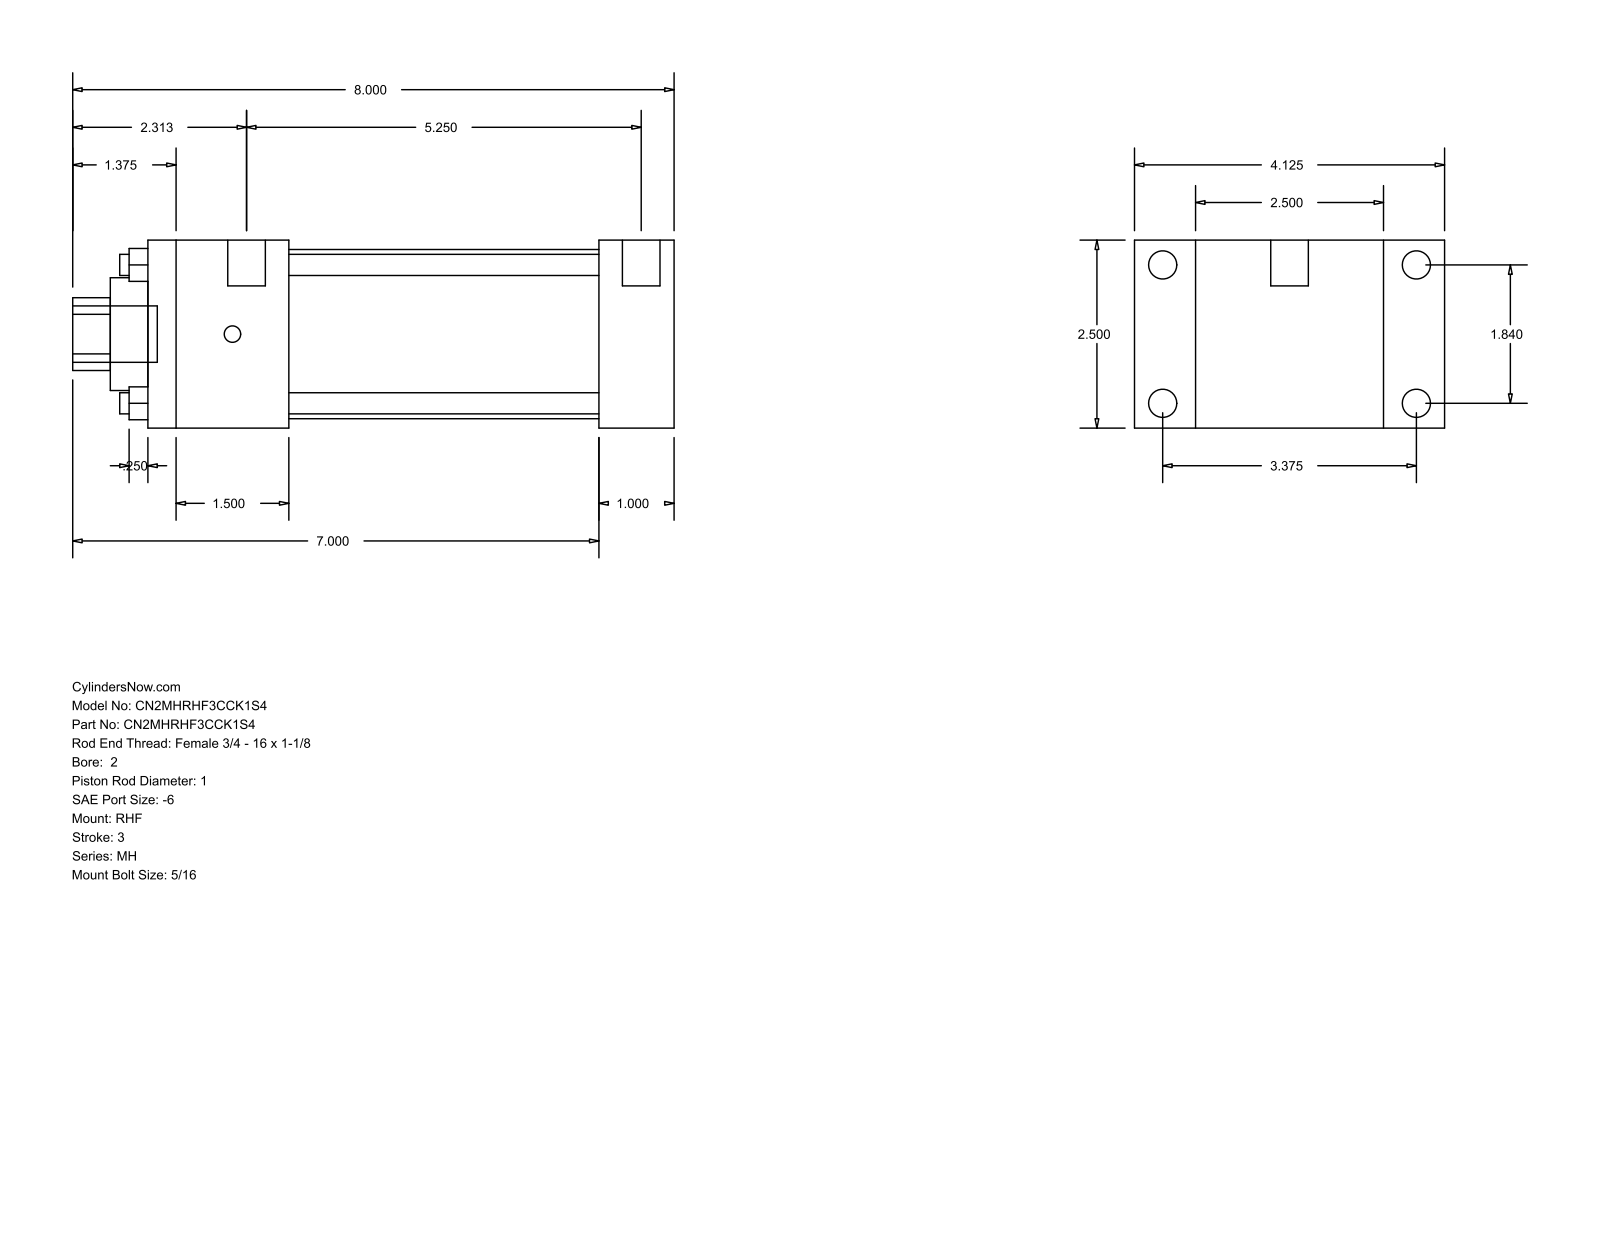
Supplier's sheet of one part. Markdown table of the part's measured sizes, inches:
| quantity | value |
| --- | --- |
| part name | MH_RHF__0200_1 |
| STEP written by | GSSL Pune (CONFIG_CONTROL_DESIGN) |
| units | inches |
| bodies | 0 solids, 88 faces (60 planar, 28 cylindrical, 0 other) |
| overall size | 8 × 4.125 × 2.5 |
| round holes (diameter × count) | 0.281 × 4, 1 × 1, 1.5 × 1, 2.25 × 1 |
| round bosses / shafts (diameter × count) | 0.375 × 4, 0.219 × 4, 0.5 × 2, 0.75 × 1 |
| partial cylindrical surfaces (radius × count) | 0.484 × 1 |
| main face-to-face distances | 2.5, 1, 0.813, 3.313, 7, 6, 4.125, 4.125, 1.875, 5.125 |
| hole center spacings | 1.301, 1.84, 2.602 |
